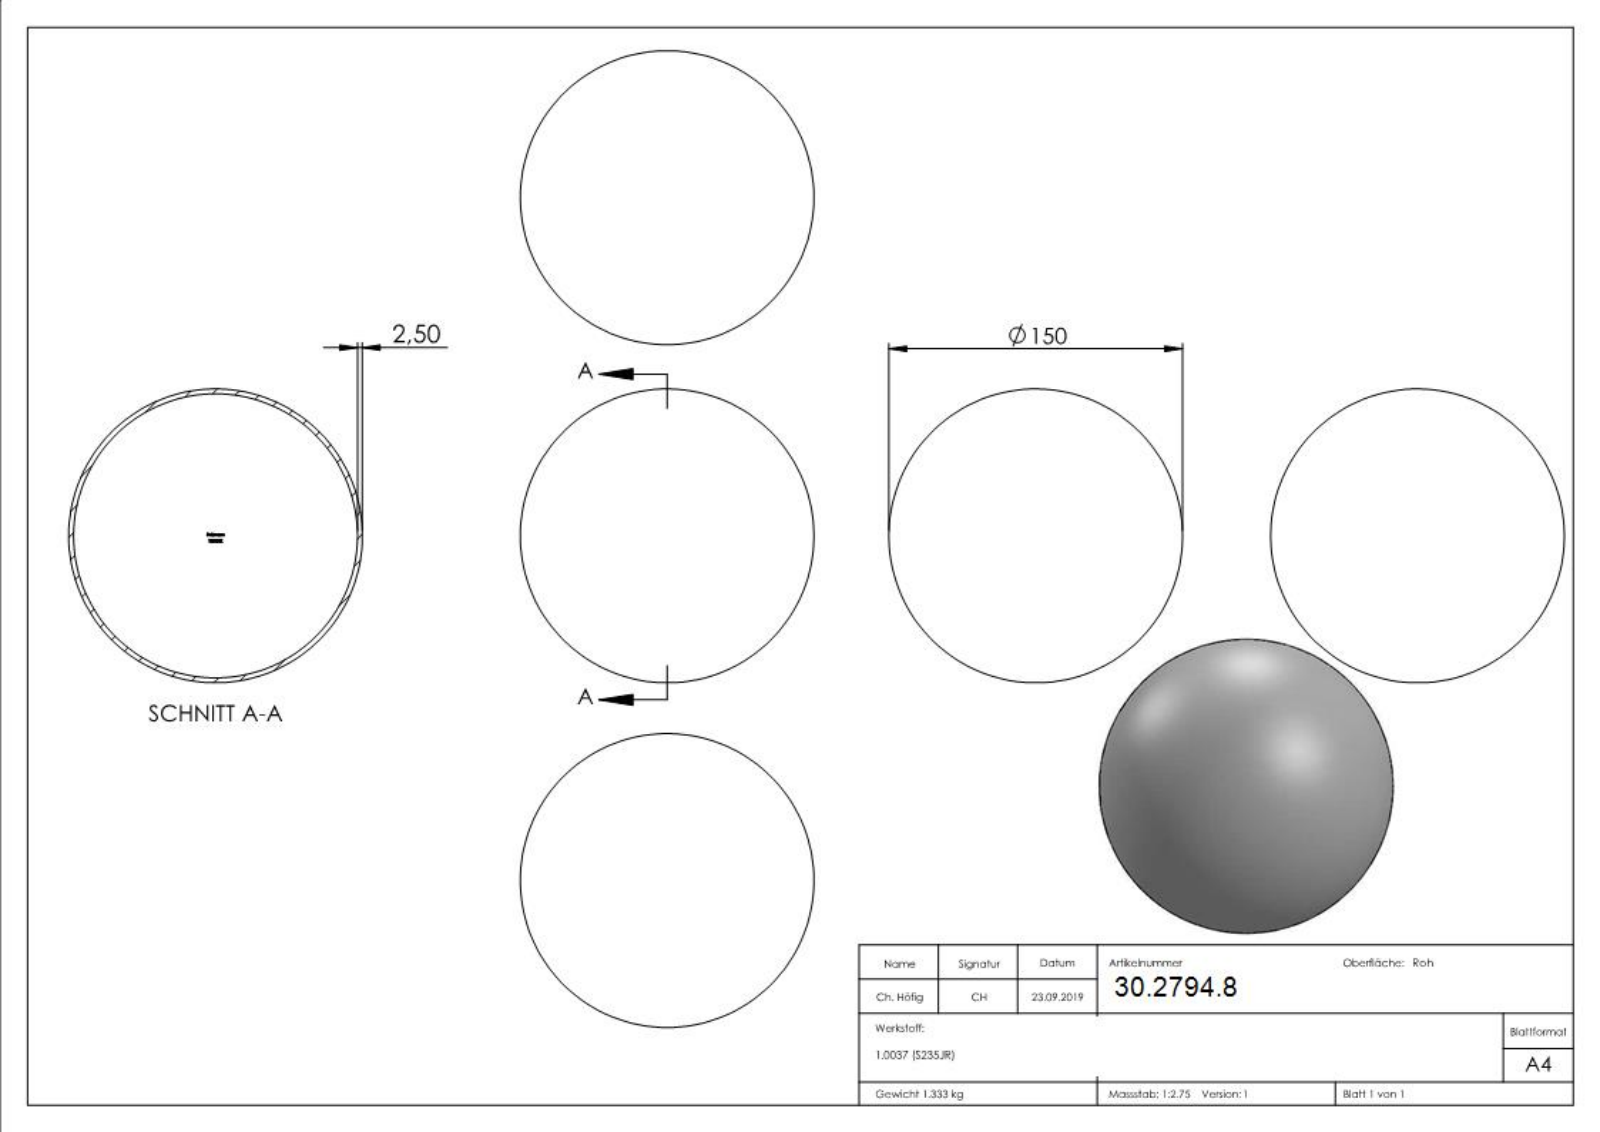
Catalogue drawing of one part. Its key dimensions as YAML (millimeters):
part_name: "150-EHK"
step_written_by: "SolidWorks 2015 (CONFIG_CONTROL_DESIGN)"
units: millimeters
bodies: {solids: 1, faces: 195, planar: 105, cylindrical: 0, other: 90}
overall_size: [150, 150, 150]
volume: 170889
surface_area: 136746
face_to_face_distances: [3.2, 1.26, 4.36, 4.5, 5.62, 0.78, 0.46, 0.54, 3.59, 2.03]
